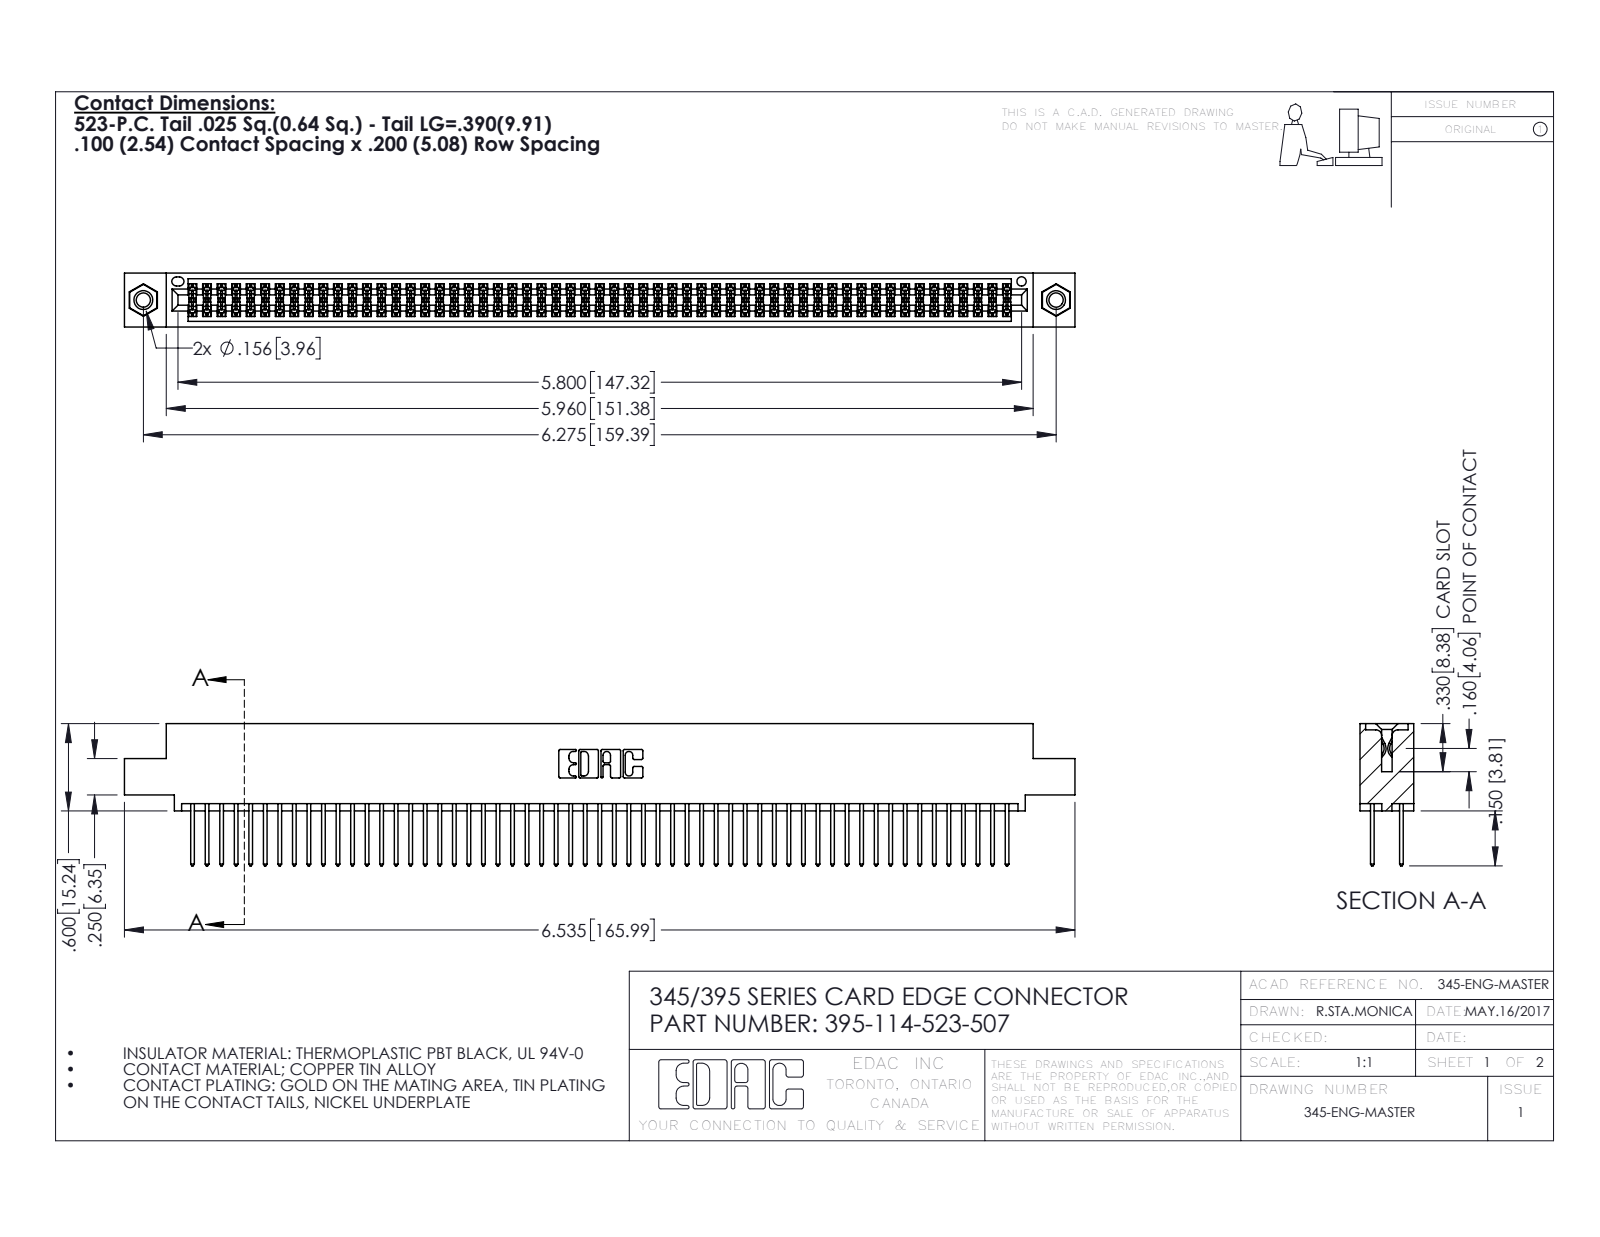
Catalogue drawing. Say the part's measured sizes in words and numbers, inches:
The part is named "345-250-001_345-250-005-103; 395-114-523-507; 345 Part_0.110 Offset - 0.156 Dia-TI; 345-292-001_345-293-123". Its 3-D file was written by "SolidWorks 2016 (CONFIG_CONTROL_DESIGN)". It is 117 solids with 5890 faces: 3878 planar, 1996 cylindrical and 16 other. Overall it measures 6.535 by 0.977 by 0.37 inches. Its volume is 1.001 cubic inches and its surface area 39.86 square inches. Round holes: 2 of diameter 0.098, 2 of diameter 0.125, 2 of diameter 0.156, 1 of diameter 0.064. Round bosses or shafts: 2 of diameter 0.155. Partial cylindrical surfaces (rounded edges, fillets, slot ends): 171 of radius 0.006, 114 of radius 0.01, 22 of radius 0.01, 6 of radius 0.007, 6 of radius 0.031, 3 of radius 0.026, 2 of radius 0.014, 2 of radius 0.019. The main face-to-face distances are 0.072, 0.298, 0.2, 0.098, 0.272, 0.025, 0.37, 0.225, 0.175, 0.149. The hole center spacings are 0.27, 6.039, 6.275.
